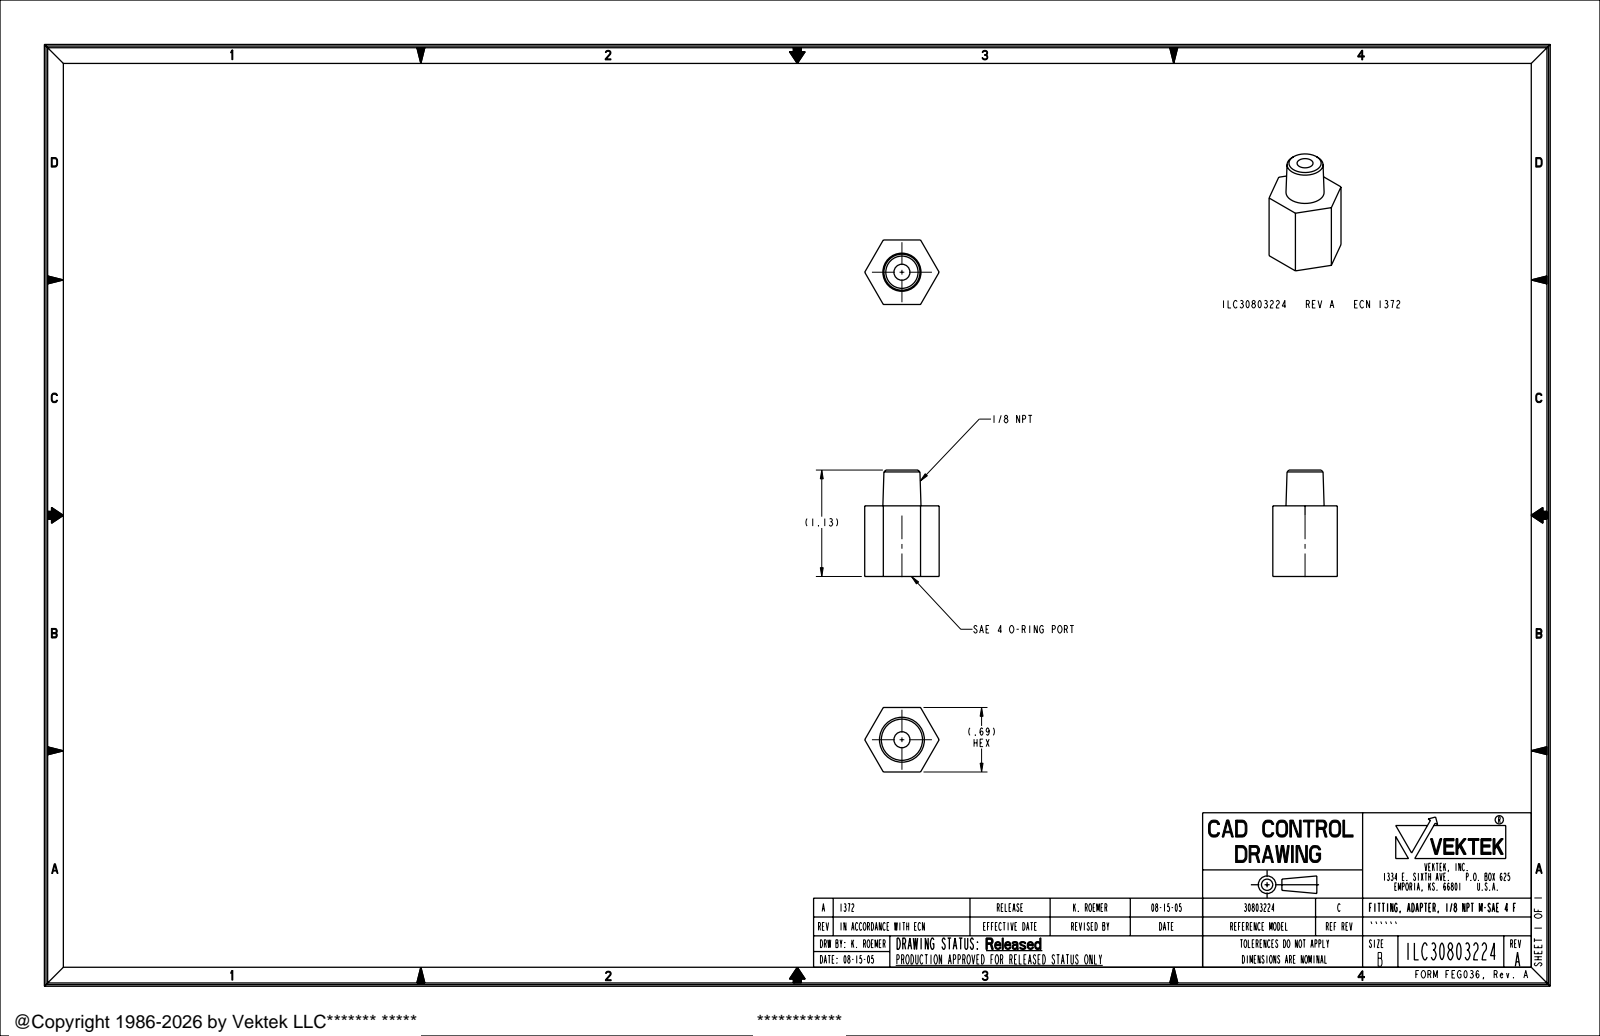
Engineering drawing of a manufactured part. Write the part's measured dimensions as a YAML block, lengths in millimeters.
part_name: "ILC30803224"
step_written_by: "PRO/ENGINEER BY PARAMETRIC TECHNOLOGY CORPORATION, 2004290 (AUTOMOTIVE_DESIGN_CC2)"
units: millimeters
bodies: {solids: 1, faces: 20, planar: 10, cylindrical: 4, other: 6}
overall_size: [28.7, 20.1, 17.4]
volume: 4160
surface_area: 2601
round_holes:
  - {diameter: 4.3, count: 1}
  - {diameter: 11.1, count: 1}
face_to_face_distances: [17.4, 19.1, 13.9, 5.2, 28.7, 14.8, 9.7]
